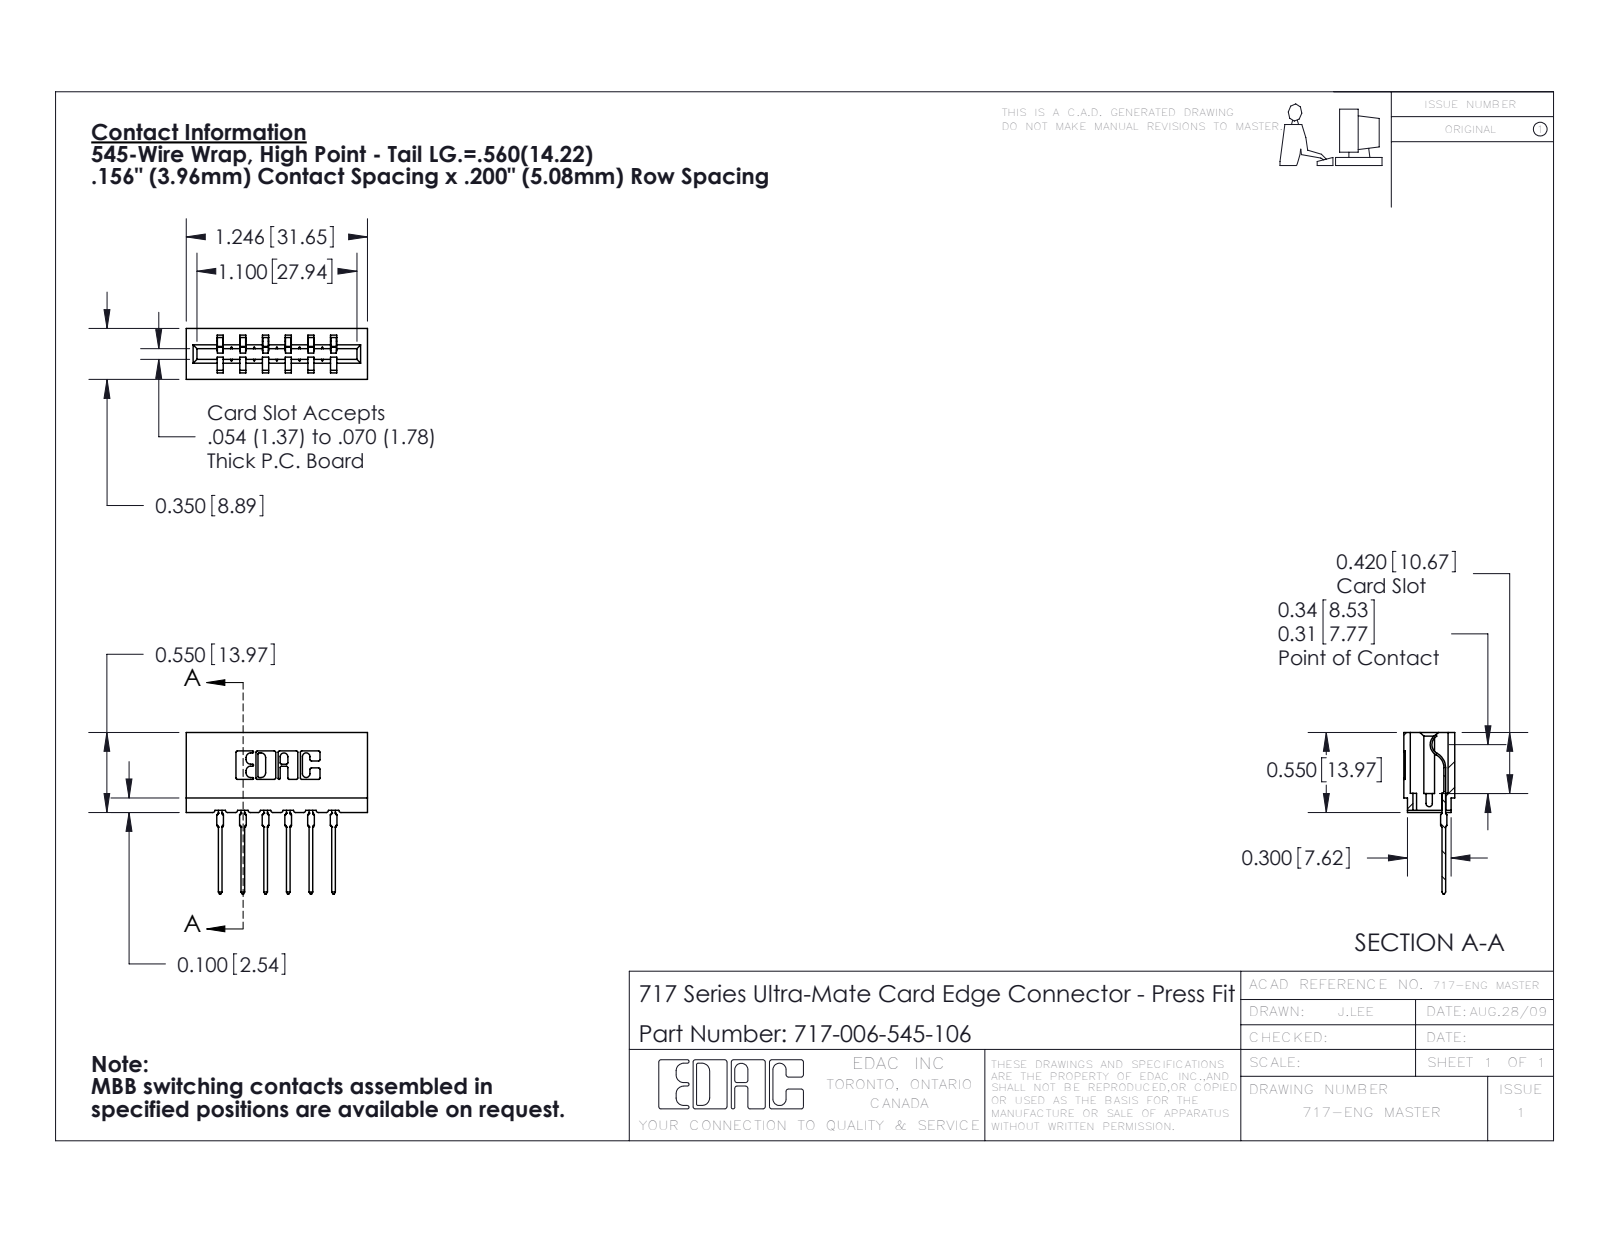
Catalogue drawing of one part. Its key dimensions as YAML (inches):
part_name: "745-292-001_545; 717-006-545-106; 717 Part_Insulator Option - 06"
step_written_by: "SolidWorks 2016 (CONFIG_CONTROL_DESIGN)"
units: inches
bodies: {solids: 7, faces: 772, planar: 462, cylindrical: 154, other: 156}
overall_size: [1.246, 1.109, 0.35]
volume: 0.174
surface_area: 5.75
partial_cylinders:
  - {radius: 0.01, count: 22}
  - {radius: 0.015, count: 12}
  - {radius: 0.021, count: 12}
  - {radius: 0.007, count: 6}
  - {radius: 0.031, count: 6}
  - {radius: 0.005, count: 4}
  - {radius: 0.011, count: 4}
  - {radius: 0.026, count: 3}
face_to_face_distances: [0.212, 0.156, 0.138, 0.35, 0.198, 0.312, 0.624, 0.042, 0.312, 0.468]
